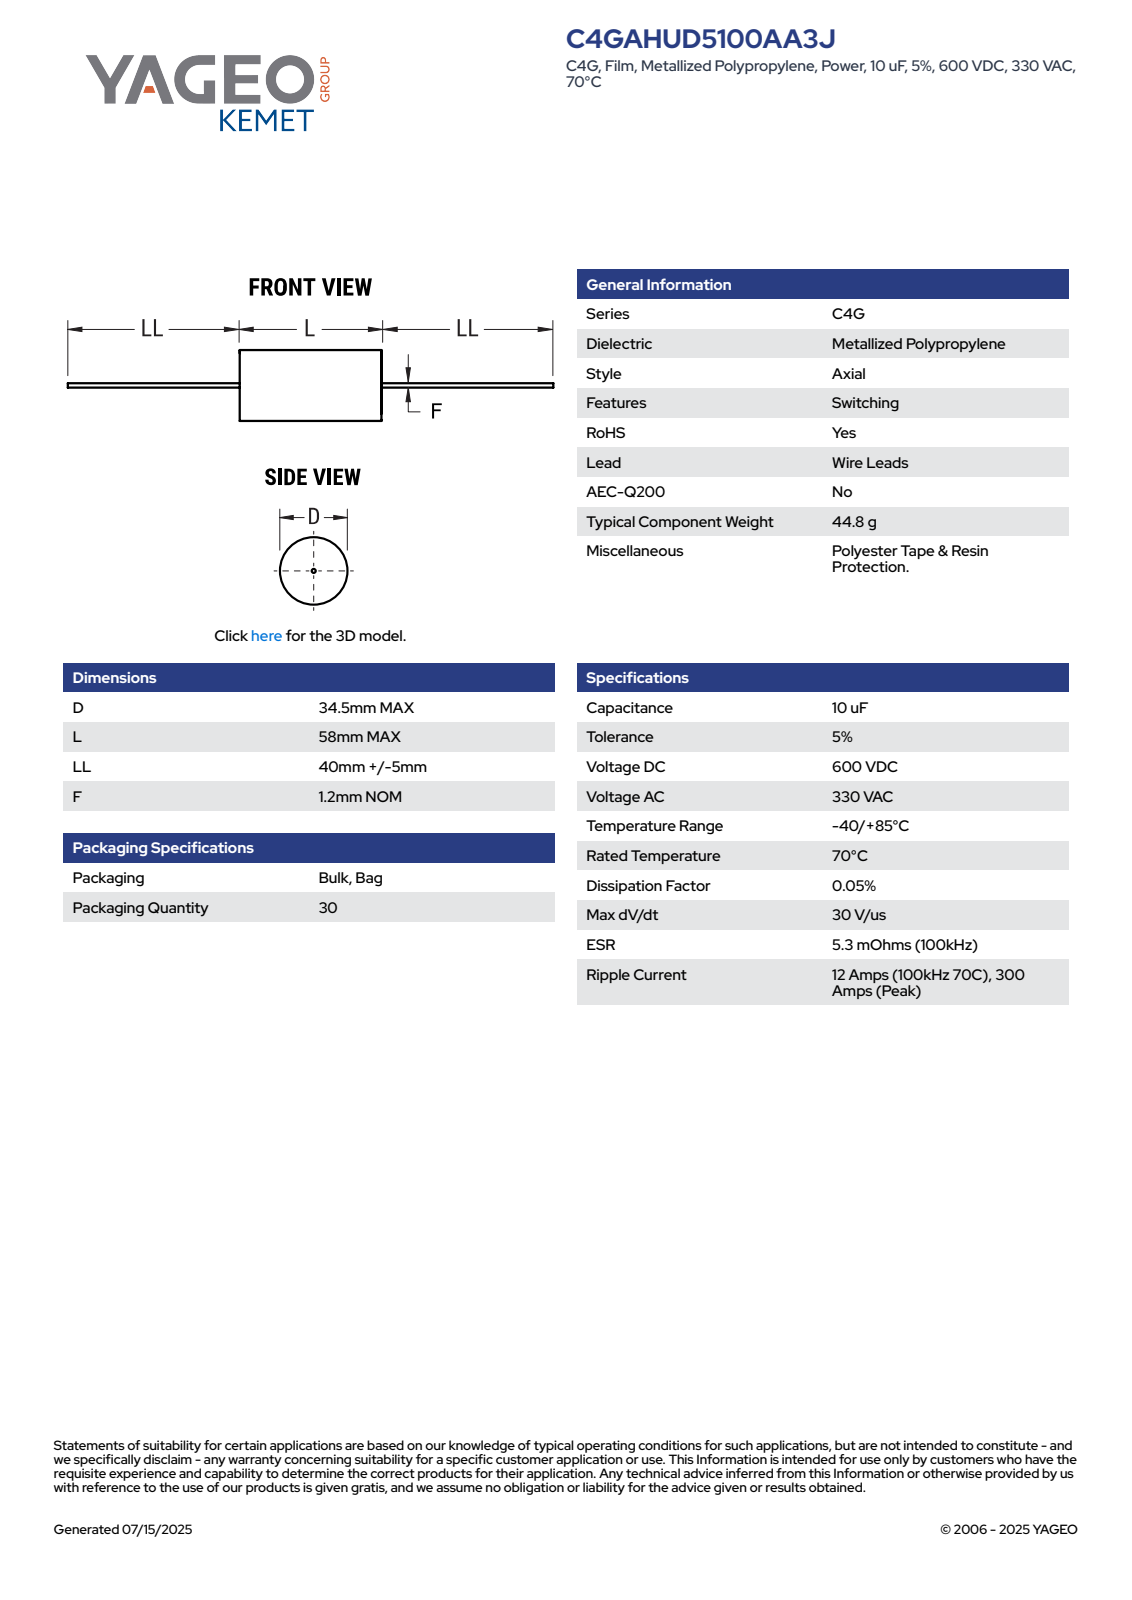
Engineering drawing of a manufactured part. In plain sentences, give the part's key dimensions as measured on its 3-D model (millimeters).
The part is named "CFP_ACWF_34.5X58_D34.5L58LL45F1.2". Its 3-D file was written by "SolidWorks 2014 (AUTOMOTIVE_DESIGN)". It is 2 solids with 87 faces: 28 planar, 28 cylindrical and 31 other. Overall it measures 148 by 34.5 by 34.5 millimeters. Its volume is 54 321 cubic millimeters and its surface area 10 364 square millimeters. Round bosses or shafts: 1 of diameter 34.5, 1 of diameter 1.2. Partial cylindrical surfaces (rounded edges, fillets, slot ends): 1 of radius 17.24. The main face-to-face distances are 58.01, 58, 45, 103, 44.99, 148, 103.01.
